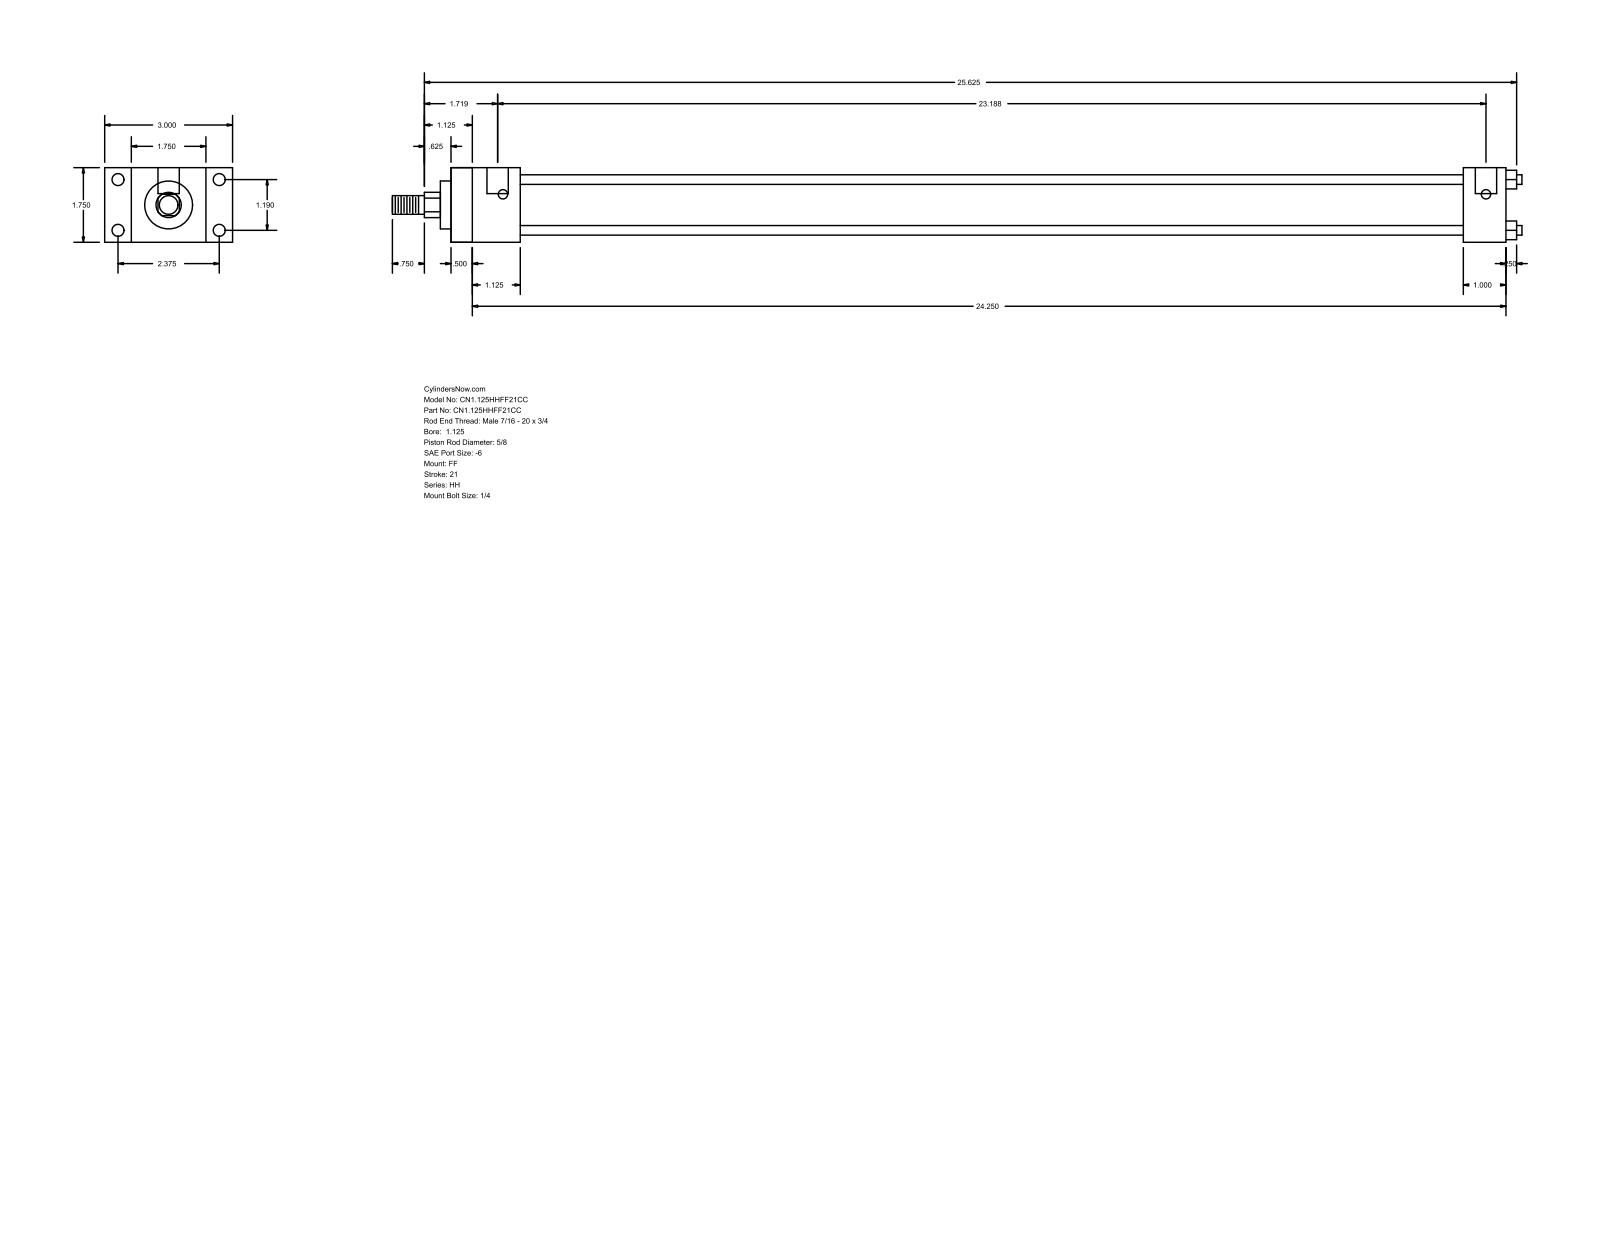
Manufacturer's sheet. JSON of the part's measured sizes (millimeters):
{"part_name": "HH_FF__0112_0.625", "step_written_by": "GSSL Pune (CONFIG_CONTROL_DESIGN)", "units": "millimeters", "bodies": {"solids": 0, "faces": 92, "planar": 64, "cylindrical": 28, "other": 0}, "overall_size": [673.1, 76.2, 44.45], "round_holes": [[5.56, 4], [7.14, 4], [12.7, 2]], "round_bosses_or_shafts": [[5.71, 4], [34.92, 1], [28.57, 1], [15.88, 1], [11.11, 1]], "partial_cylinders_radius": [[7.54, 1]], "face_to_face_distances": [44.46, 628.64, 12.69, 615.95, 15.87, 28.58, 60.33, 25.4, 41.27, 603.24], "hole_center_spacings": [30.22, 60.32, 67.47, 585.79, 3.17, 588.96]}
